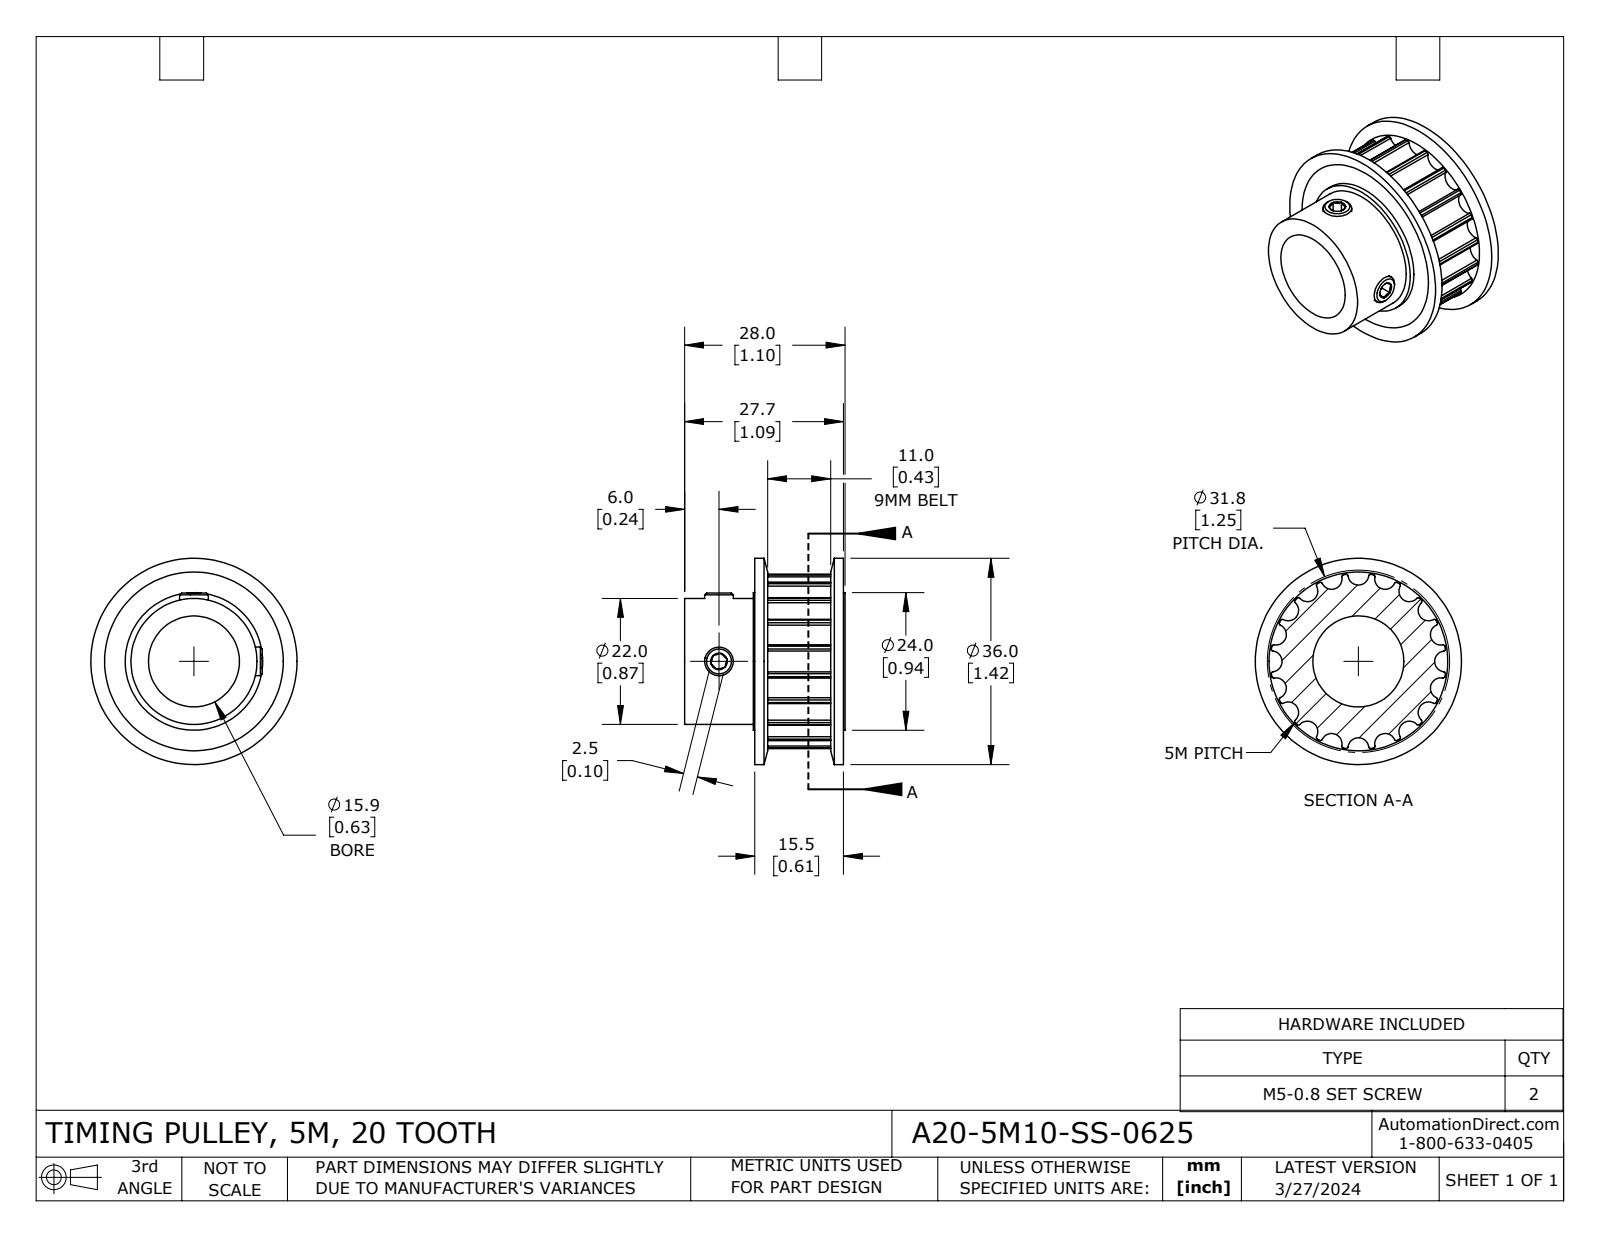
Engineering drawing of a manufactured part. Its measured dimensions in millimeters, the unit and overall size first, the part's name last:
Units: millimetres
Overall size (bounding box): 36 × 36 × 28
Round holes (diameter × count): ⌀4.2 ×2, ⌀15.88 ×1, ⌀24 ×1
Round bosses / shafts (diameter × count): ⌀5 ×2, ⌀36 ×1, ⌀22 ×1
Partial cylindrical surfaces — rounded edges, fillets, slot ends (radius × count): R0.3 ×40, R1.82 ×20, R15.35 ×1
Main face-to-face distances: 1.6, 12.6, 11, 2.5, 0.9, 13.5, 15.1, 14.2, 28, 27.1
Volume: 9 980 mm³ · Surface area: 8 083 mm²
Bodies: 5 solids, 182 faces (25 planar, 123 cylindrical, 34 other)
Part name (STEP PRODUCT): A20-5M10-SS-0625
STEP written by: SolidWorks 2021 (CONFIG_CONTROL_DESIGN)
